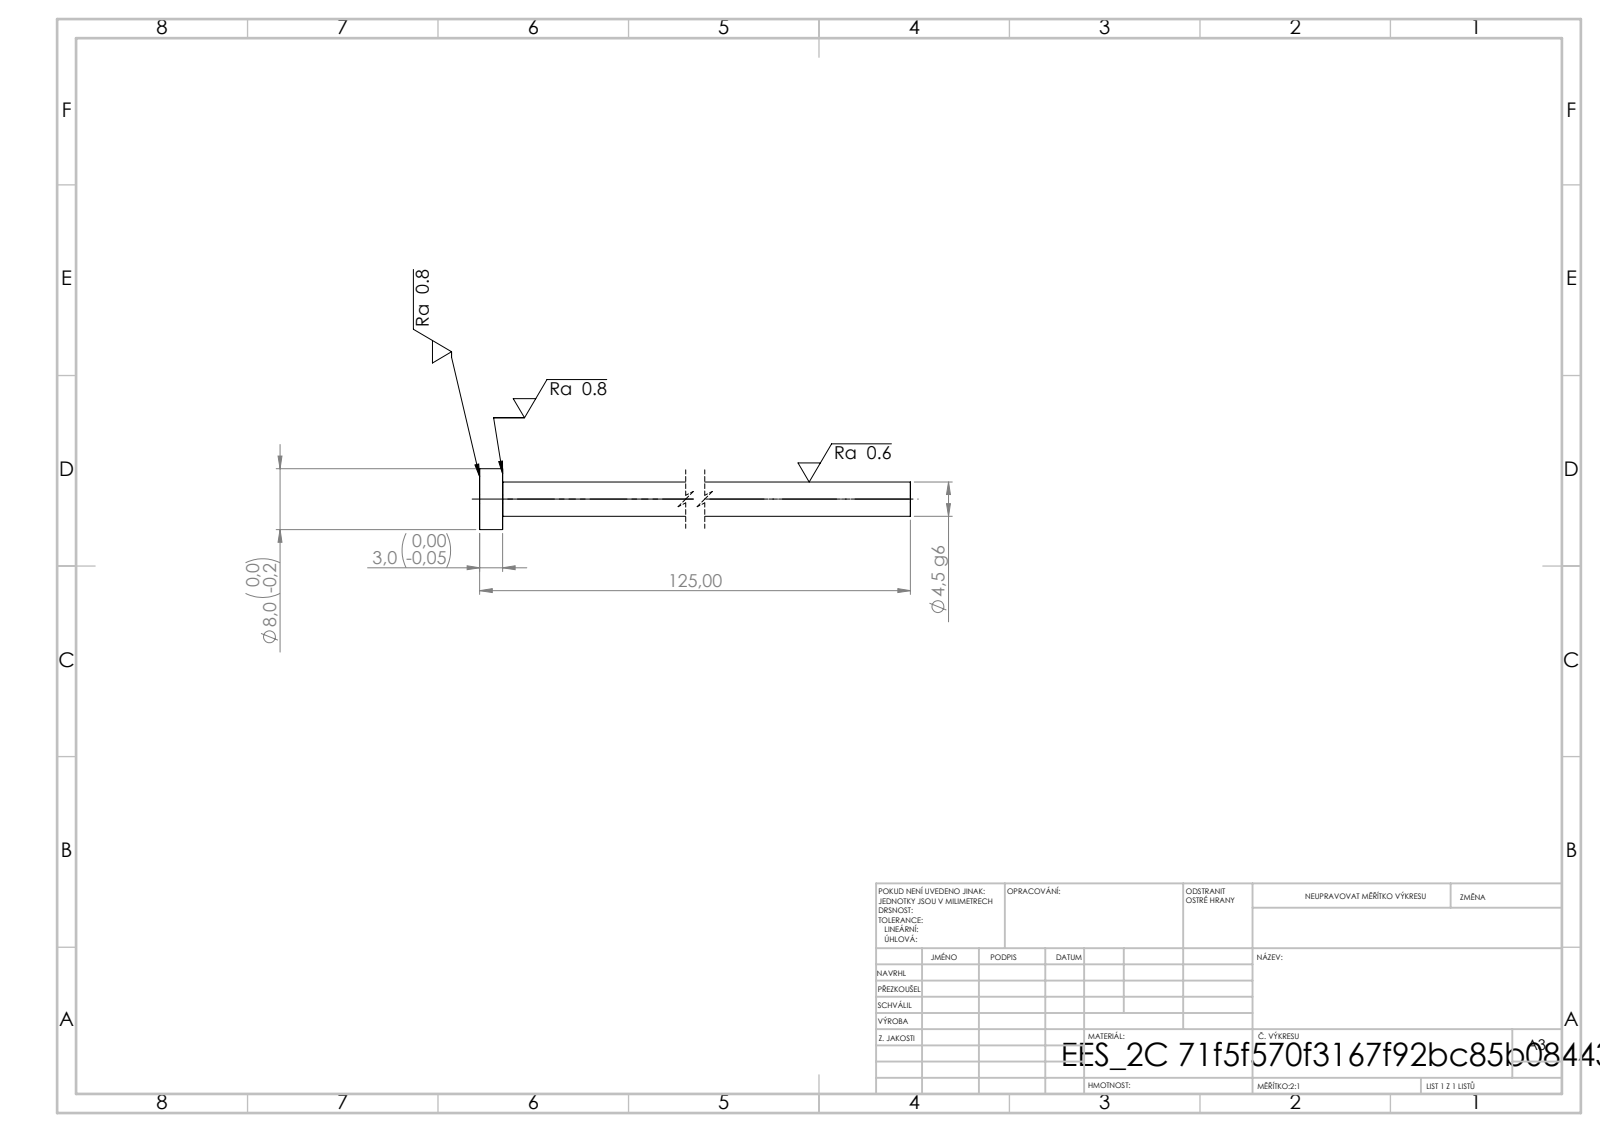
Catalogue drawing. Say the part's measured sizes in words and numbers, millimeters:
Its 3-D file was written by "SolidWorks 2019 (CONFIG_CONTROL_DESIGN)". It is 1 solid with 7 faces: 3 planar, 4 cylindrical and 0 other. Overall it measures 125 by 8 by 8 millimeters. Its volume is 2 091 cubic millimeters and its surface area 1 901 square millimeters. Round bosses or shafts: 1 of diameter 8, 1 of diameter 4.5. The main face-to-face distances are 3, 125, 122.
